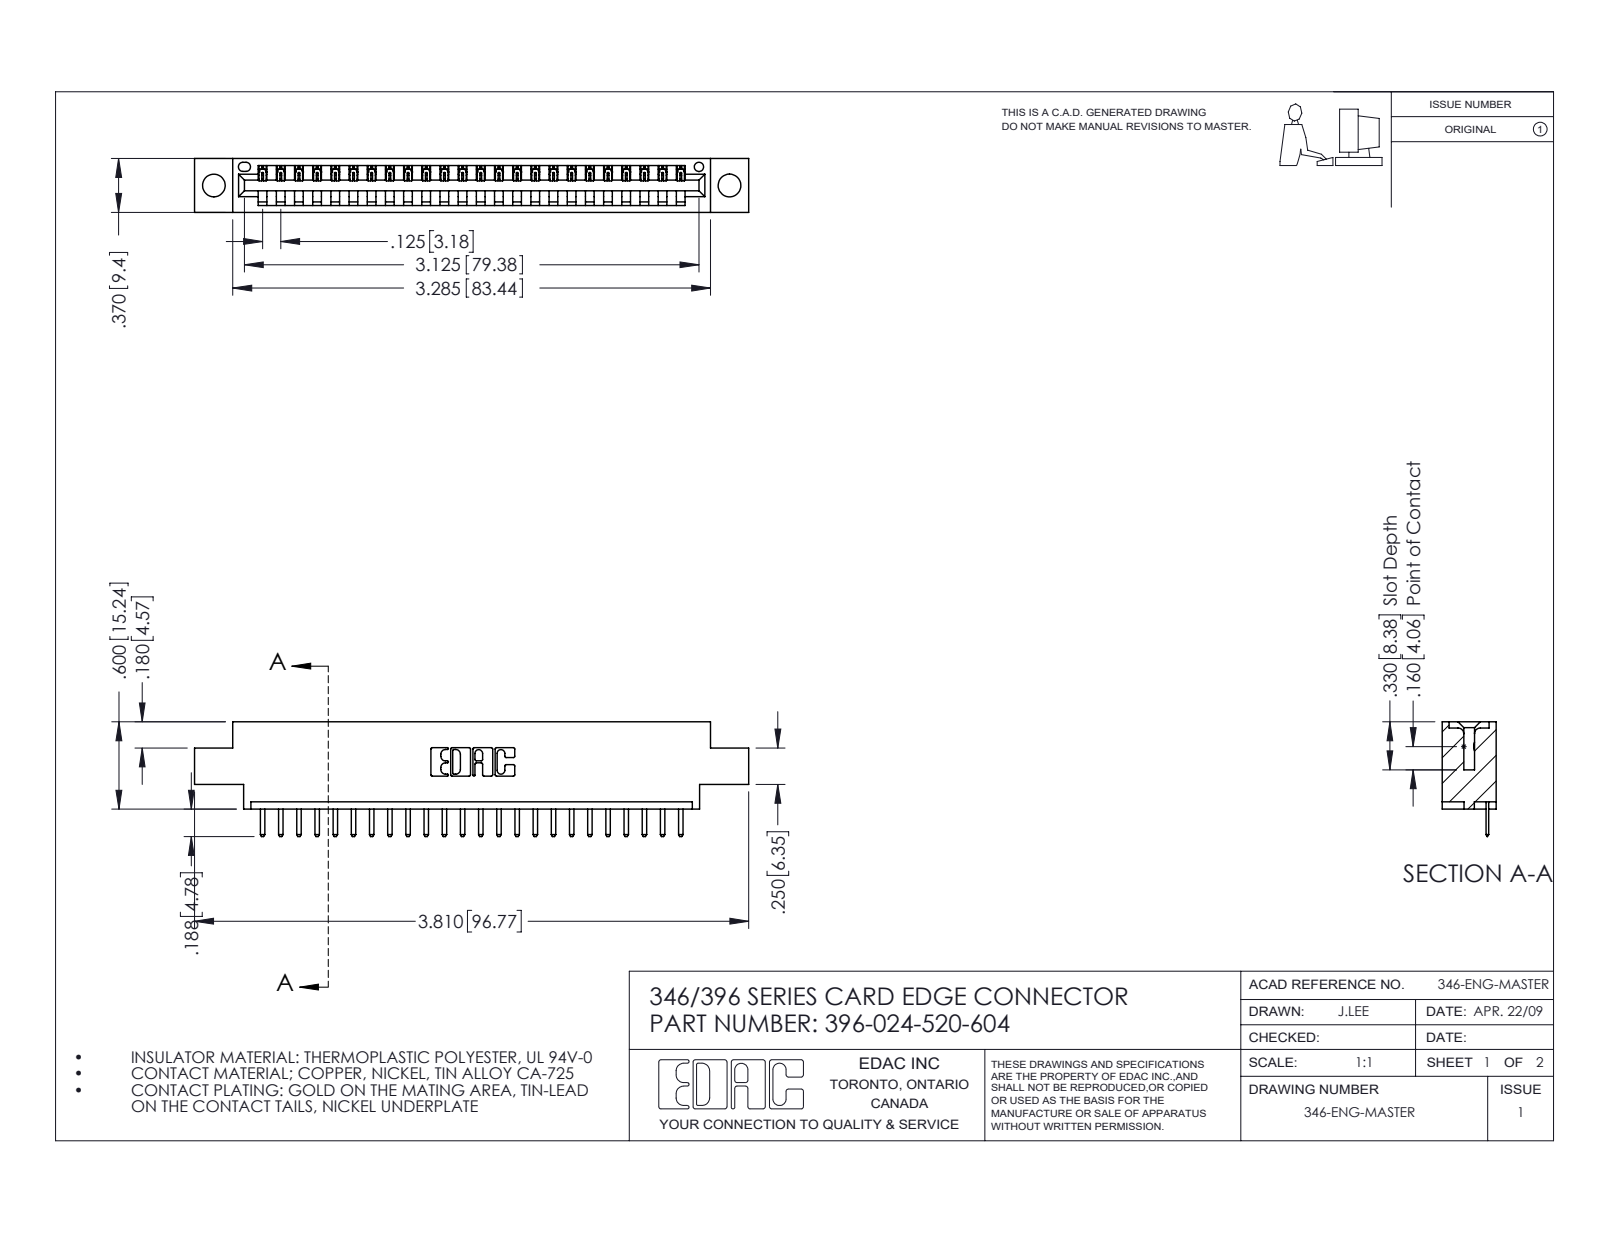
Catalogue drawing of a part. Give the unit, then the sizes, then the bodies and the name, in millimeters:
Units: millimetres
Overall size (bounding box): 96.8 × 20 × 9.4
Round holes (diameter × count): ⌀4 ×2, ⌀1.6 ×1
Partial cylindrical surfaces — rounded edges, fillets, slot ends (radius × count): R0.3 ×50, R0.2 ×48, R0.3 ×22, R0.2 ×6, R0.8 ×6, R0.7 ×3, R0.8 ×2, R1 ×2
Main face-to-face distances: 9.4, 1.2, 8.2, 6.4, 3.8, 5.6, 2.5, 4.4, 1.8, 7.6
Hole centre spacings: 6.2, 84.8, 90
Volume: 8 830 mm³ · Surface area: 10 570 mm²
Bodies: 25 solids, 1614 faces (1088 planar, 526 cylindrical, 0 other)
Part name (STEP PRODUCT): 345-292-001_345-293-120; 346 Part_0.170 Offset - 0.156 Dia-TH; 396-024-520-604
STEP written by: SolidWorks 2016 (CONFIG_CONTROL_DESIGN)
